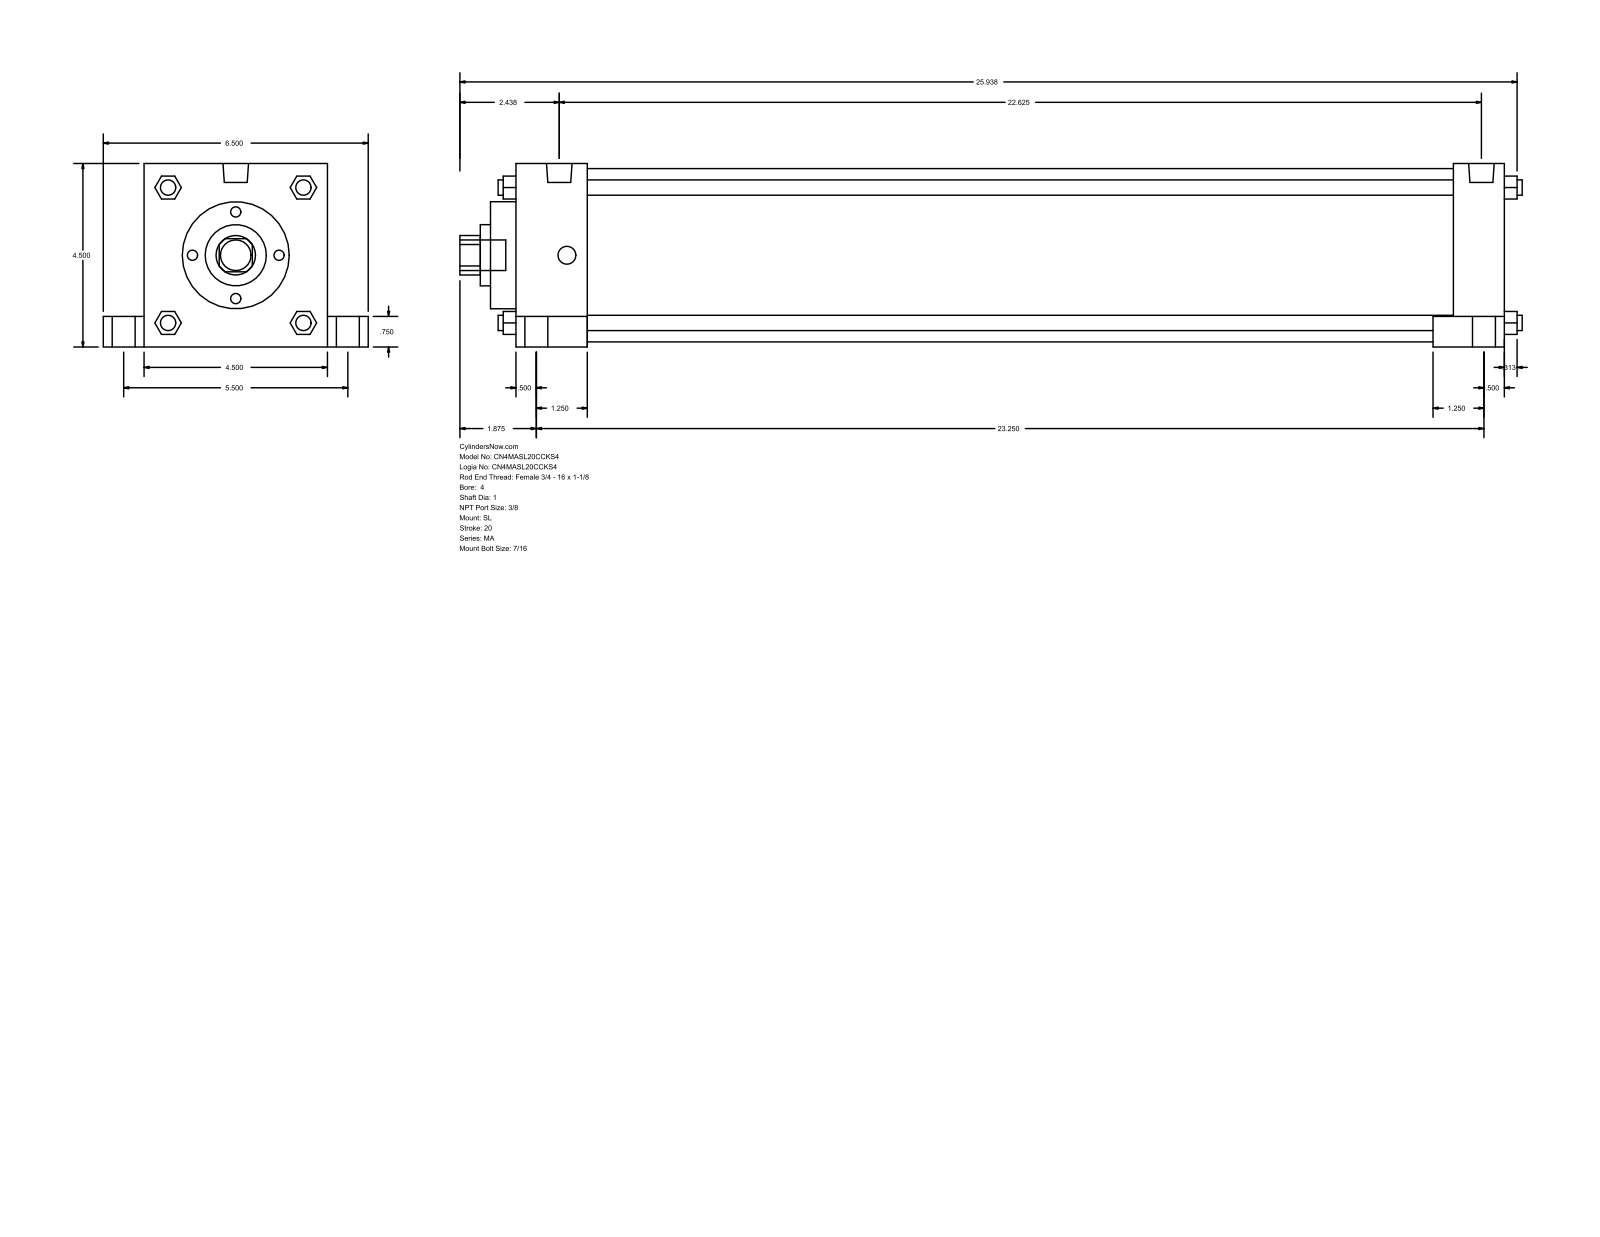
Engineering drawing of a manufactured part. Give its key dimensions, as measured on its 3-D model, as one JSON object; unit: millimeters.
{"part_name": "MA_SL__0400_1", "step_written_by": "GSSL Pune (CONFIG_CONTROL_DESIGN)", "units": "millimeters", "bodies": {"solids": 0, "faces": 150, "planar": 113, "cylindrical": 37, "other": 0}, "overall_size": [661.99, 165.1, 114.3], "round_holes": [[25.4, 1], [38.1, 1], [66.67, 1], [107.95, 1]], "round_bosses_or_shafts": [[20.64, 4], [14.29, 4], [11.11, 4], [9.53, 4], [15.93, 2], [19.05, 1]], "partial_cylinders_radius": [[12.29, 1]], "face_to_face_distances": [114.3, 615.96, 44.46, 571.5, 584.2, 539.74, 31.76, 25.4, 139.7, 19.05]}
